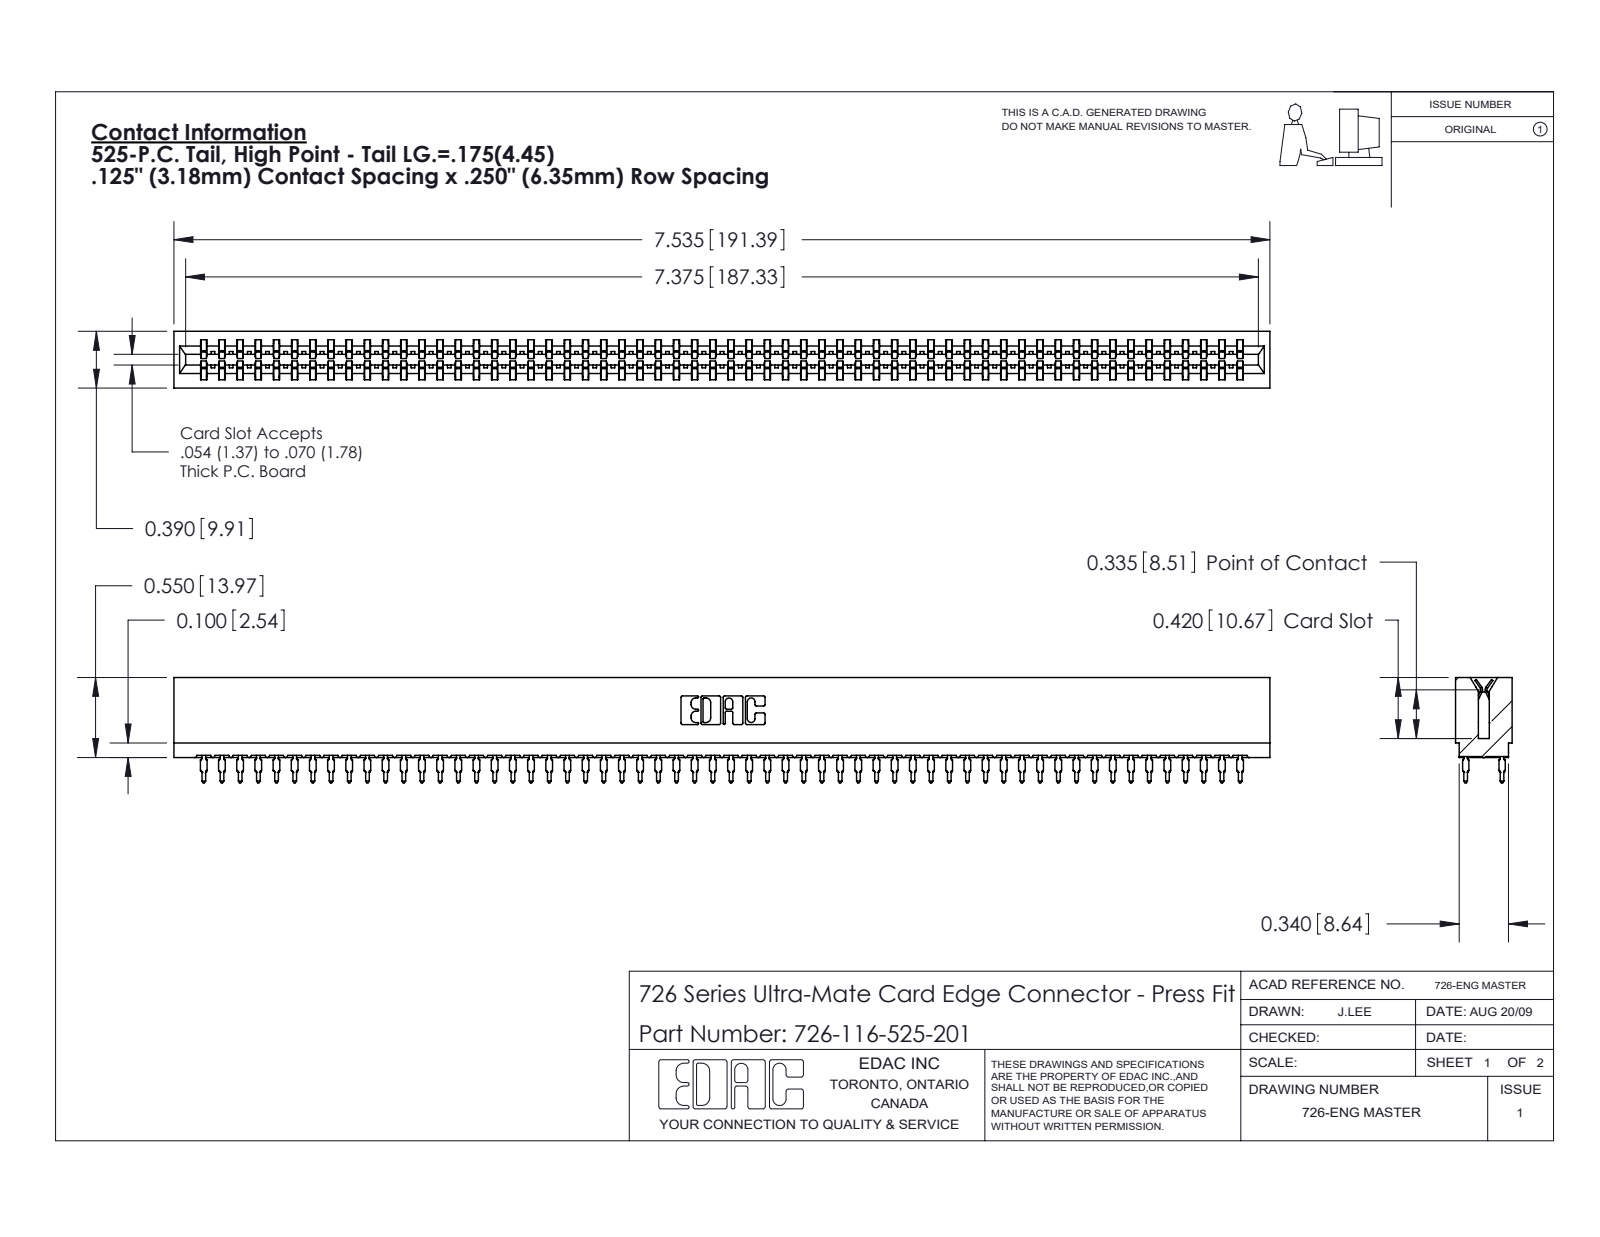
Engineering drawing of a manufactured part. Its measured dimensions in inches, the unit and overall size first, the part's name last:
Units: inches
Overall size (bounding box): 7.535 × 0.724 × 0.39
Partial cylindrical surfaces — rounded edges, fillets, slot ends (radius × count): R0.021 ×232, R0.015 ×59, R0.01 ×22, R0.005 ×8, R0.011 ×8, R0.007 ×6, R0.031 ×6, R0.026 ×3
Main face-to-face distances: 0.057, 0.333, 0.39, 0.025, 0.307, 0.275, 0.25, 0.083, 0.365, 0.032
Volume: 1.066 in³ · Surface area: 45.15 in²
Bodies: 117 solids, 10479 faces (5391 planar, 2072 cylindrical, 3016 other)
Part name (STEP PRODUCT): 726 Part_.515 Slot Depth - 01; 726-116-525-201; 746-292-001_525
STEP written by: SolidWorks 2020 (CONFIG_CONTROL_DESIGN)
